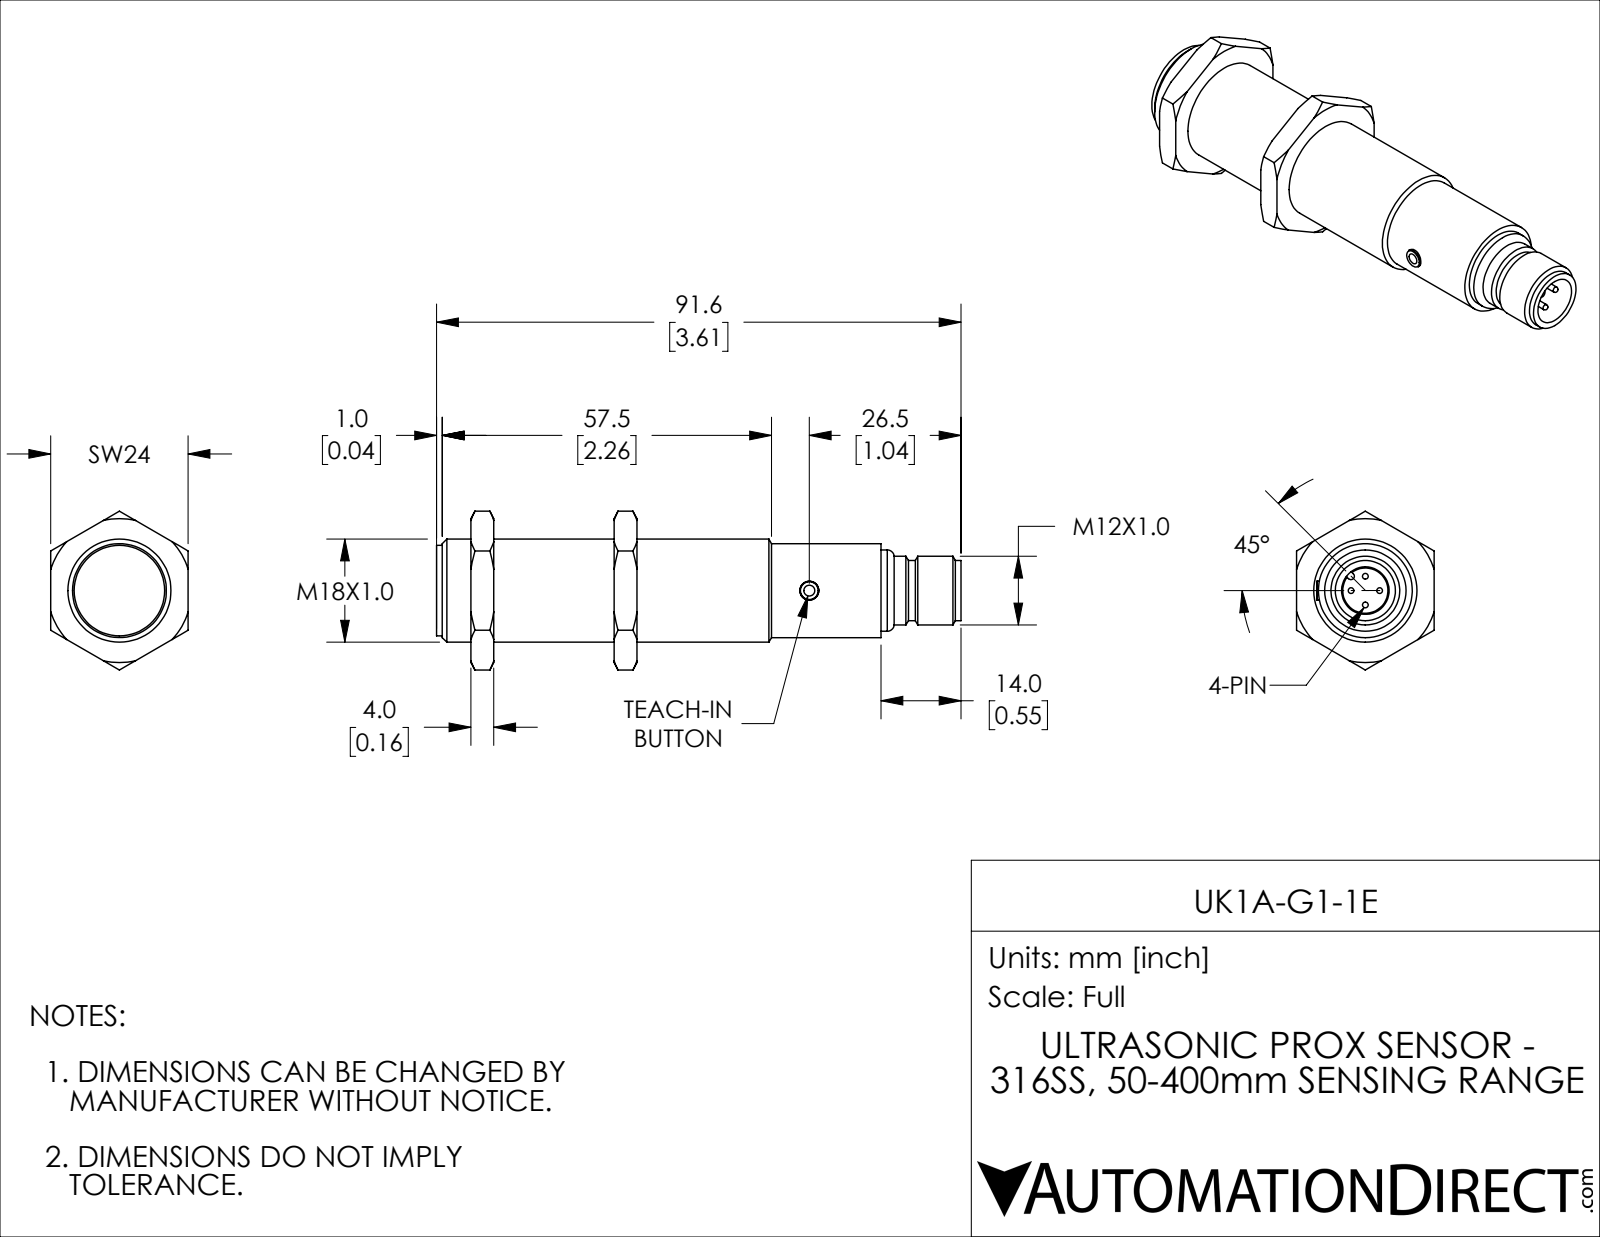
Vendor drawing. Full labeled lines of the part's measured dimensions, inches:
Part name (STEP PRODUCT): UK1A-G1-1E
STEP written by: SolidWorks 2018 (AUTOMOTIVE_DESIGN)
Units: inches
Bodies: 4 solids, 113 faces (27 planar, 35 cylindrical, 51 other)
Overall size (bounding box): 3.606 × 1.091 × 0.945
Volume: 1.338 in³ · Surface area: 11.97 in²
Round holes (diameter × count): ⌀0.13 ×1, ⌀0.327 ×1, ⌀0.709 ×1
Round bosses / shafts (diameter × count): ⌀0.039 ×4, ⌀0.646 ×1, ⌀0.622 ×1, ⌀0.559 ×1, ⌀0.472 ×1, ⌀0.413 ×1
Partial cylindrical surfaces — rounded edges, fillets, slot ends (radius × count): R0.024 ×1
Main face-to-face distances: 0.984, 0.157, 0.945, 1.142, 0.827, 0.236, 0.394, 1.22, 1.378, 3.055
